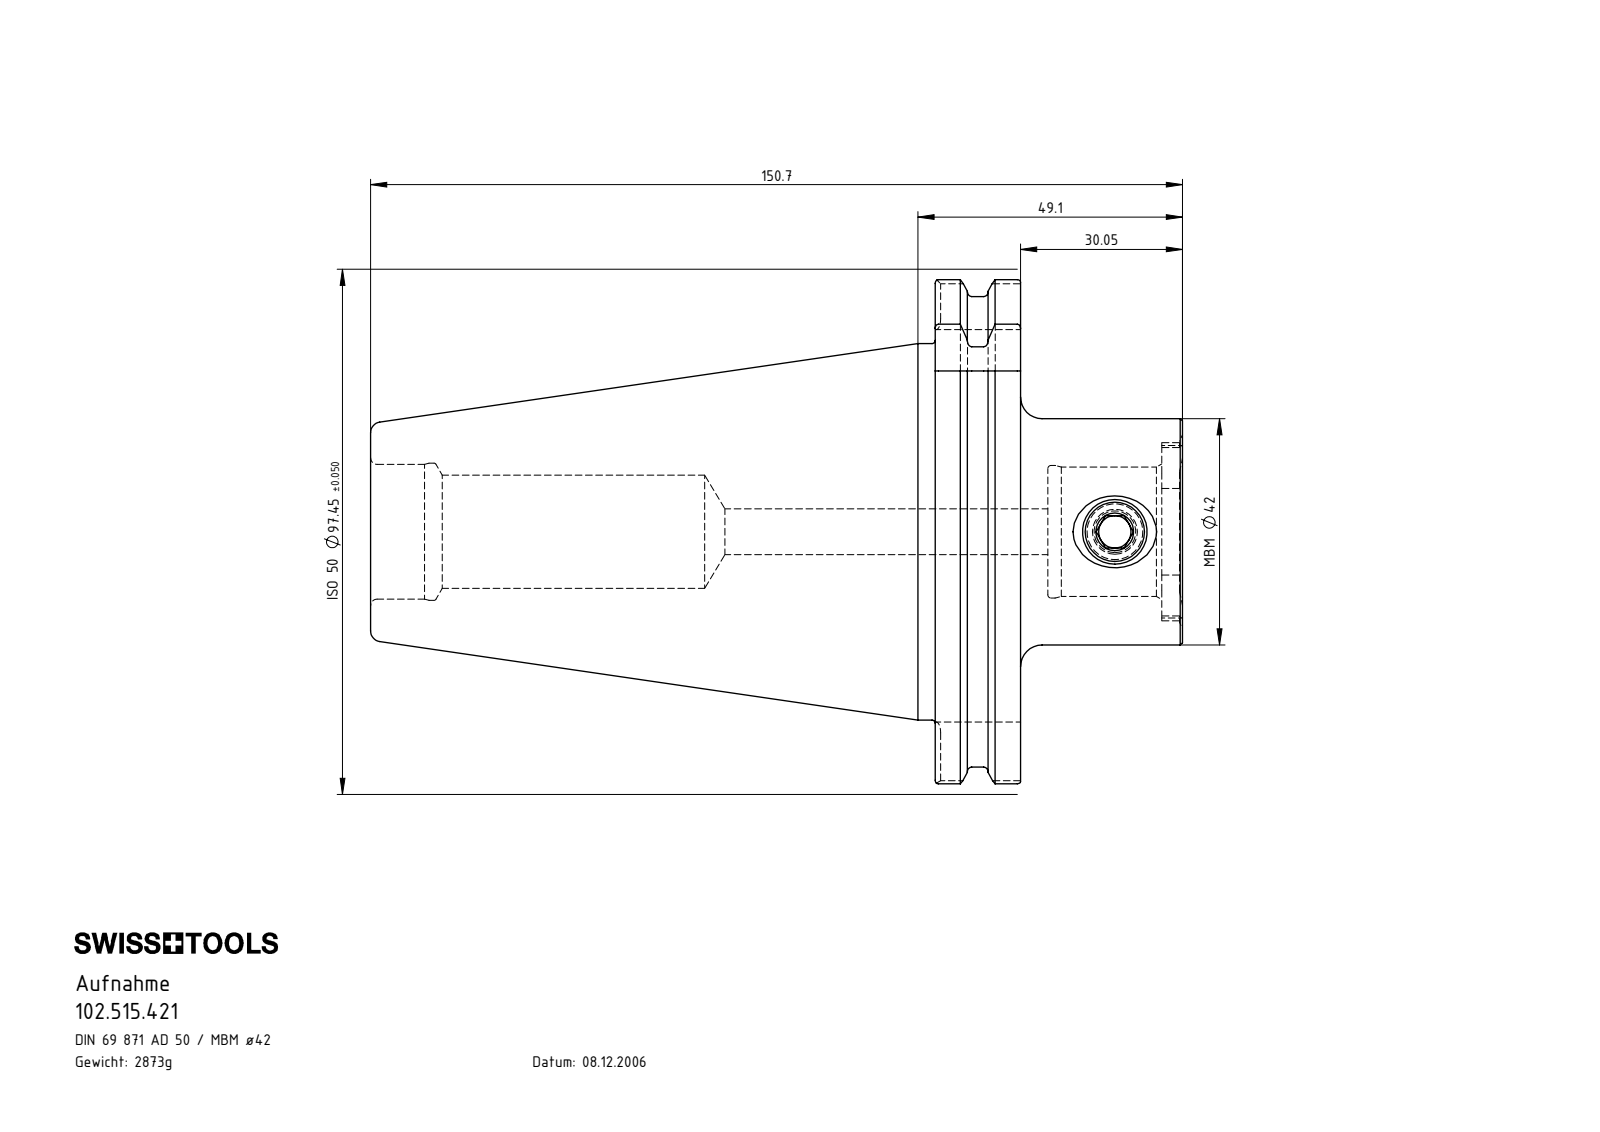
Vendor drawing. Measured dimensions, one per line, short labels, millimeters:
name: SK5-MB4.K01.049_C; MB4-ER1.001.013_A; 102.515.421
written by: SolidWorks 2017 (CONFIG_CONTROL_DESIGN)
unit: mm
bodies: 2 solids, 172 faces (55 planar, 50 cylindrical, 67 other)
size: 150.7 × 97.45 × 93.51
volume: 365 925 mm³; area: 47 682 mm²
holes: 1× ⌀6, 1× ⌀8.5, 1× ⌀11, 1× ⌀21, 1× ⌀24, 1× ⌀24.6, 1× ⌀25, 1× ⌀25.45
bosses: 1× ⌀91, 1× ⌀69.85, 1× ⌀42, 1× ⌀12
rounds: 8× R2, 4× R5.2, 1× R14.9, 1× R16.52, 1× R48.73
face distances: 15.85, 104.8, 120.65, 21.15, 125.7, 20.9, 5.05, 72.8, 146.85, 42.05
